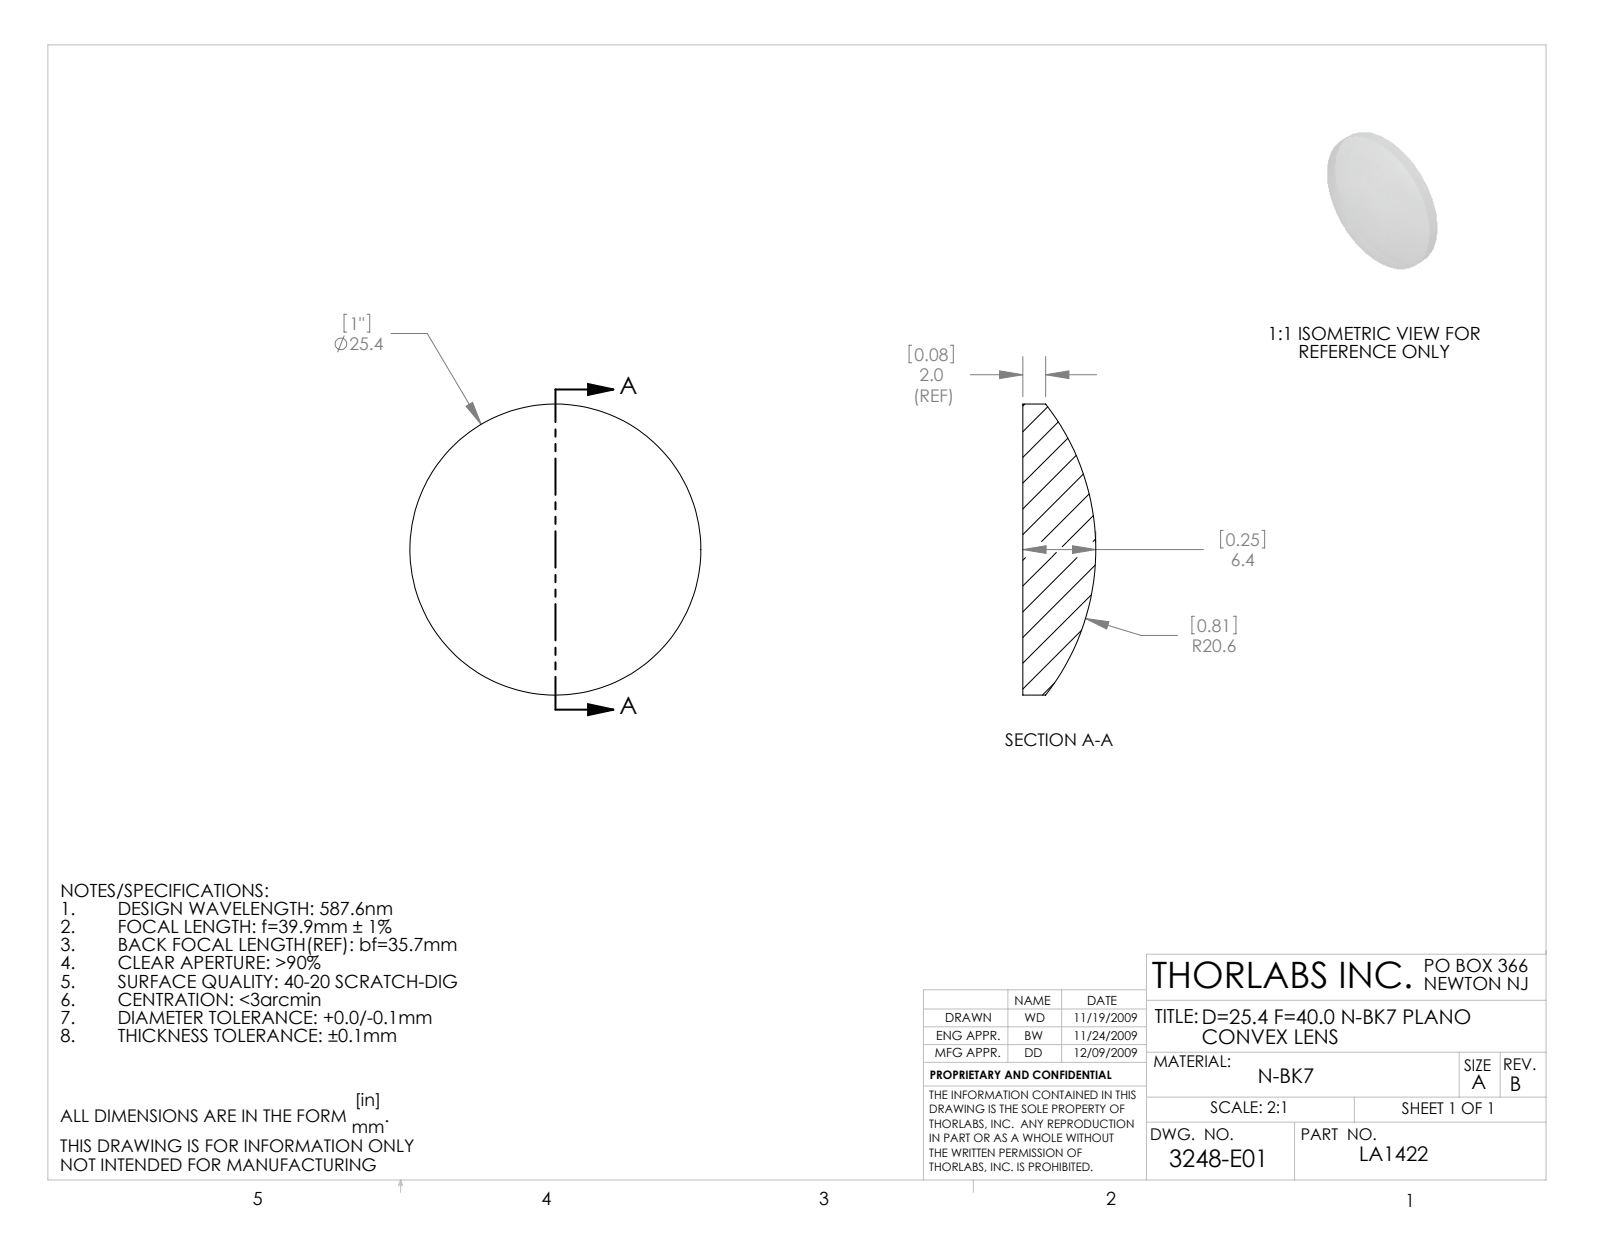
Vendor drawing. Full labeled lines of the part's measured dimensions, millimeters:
Part name (STEP PRODUCT): 3248-E0W
STEP written by: SolidWorks 2009 (AUTOMOTIVE_DESIGN)
Units: millimetres
Bodies: 1 solid, 5 faces (1 planar, 2 cylindrical, 2 other)
Overall size (bounding box): 25.4 × 25.4 × 6.37
Volume: 2 162 mm³ · Surface area: 1 232 mm²
Round bosses / shafts (diameter × count): ⌀25.4 ×1
